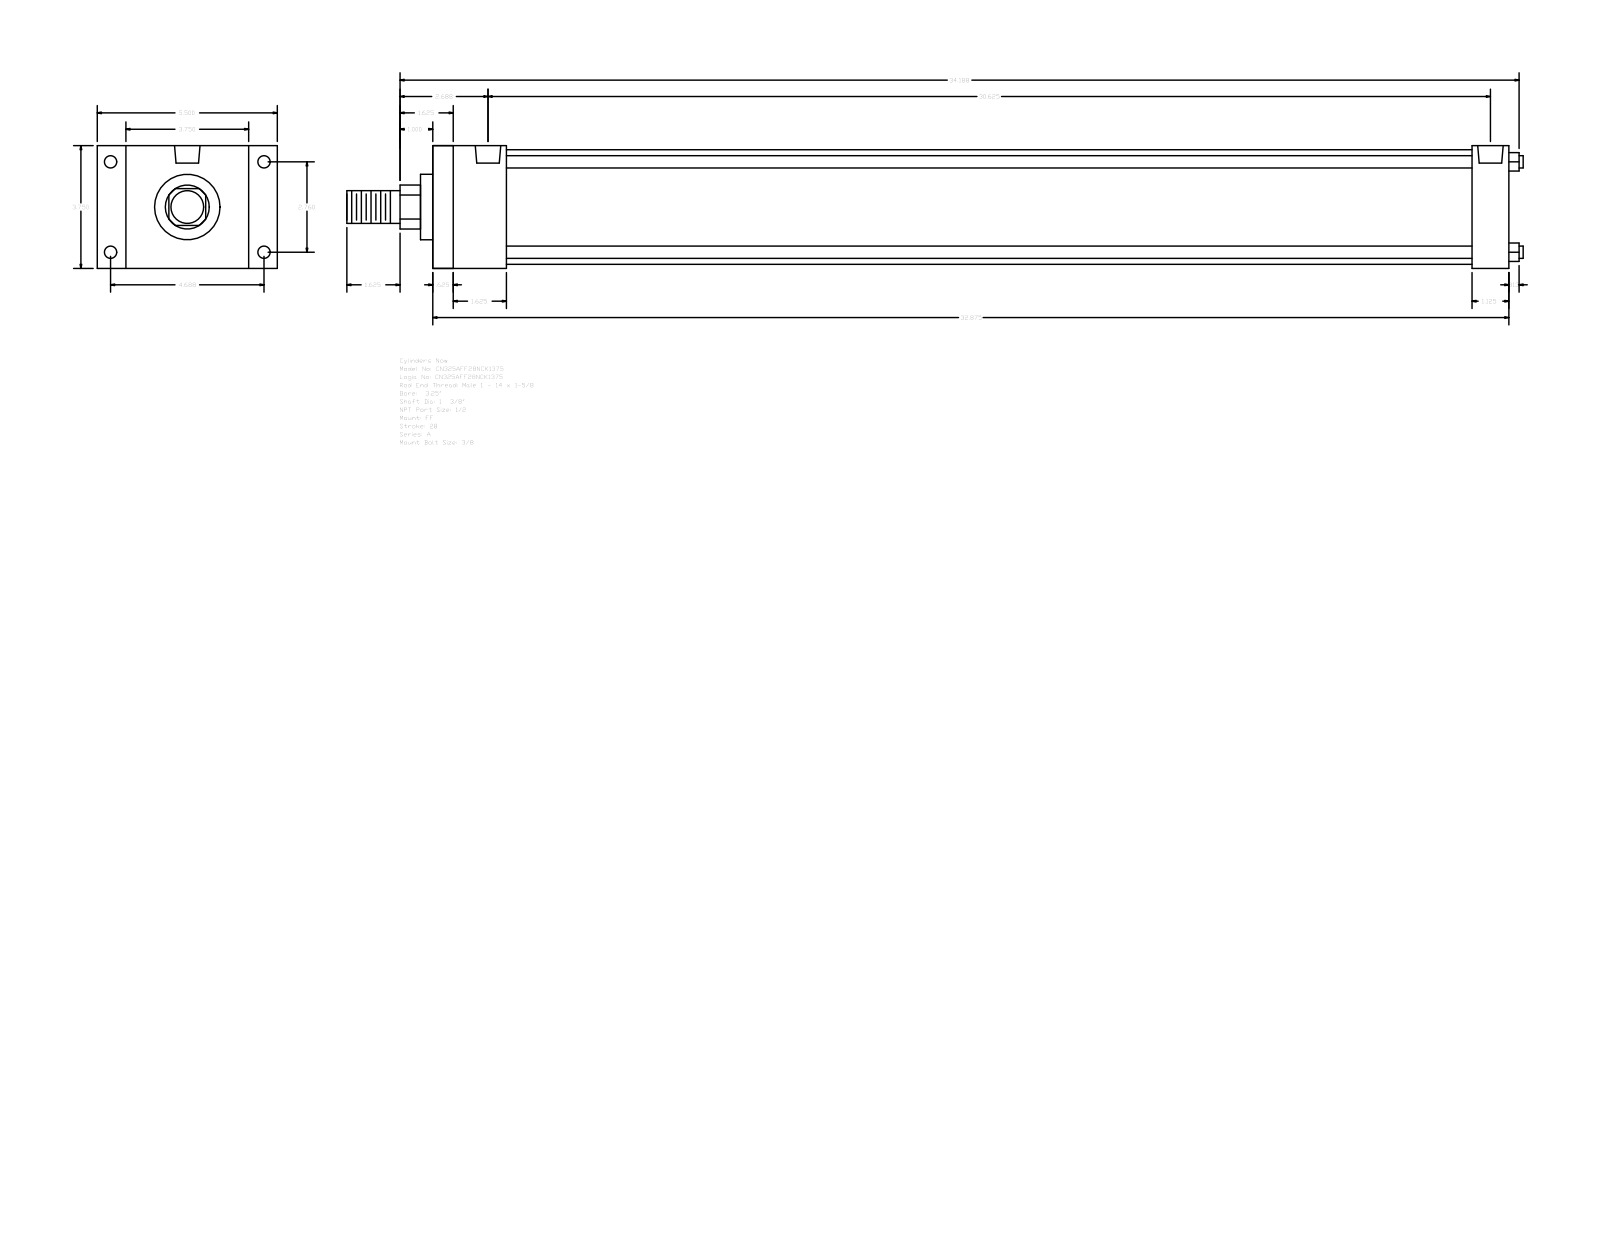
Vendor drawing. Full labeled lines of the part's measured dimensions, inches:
Part name (STEP PRODUCT): A_FF__0325_1.375
STEP written by: GSSL Pune (CONFIG_CONTROL_DESIGN)
Units: inches
Bodies: 0 solids, 92 faces (64 planar, 28 cylindrical, 0 other)
Overall size (bounding box): 35.937 × 5.5 × 3.75
Round holes (diameter × count): ⌀0.344 ×4, ⌀0.375 ×4, ⌀0.778 ×2
Round bosses / shafts (diameter × count): ⌀0.375 ×4, ⌀3.5 ×1, ⌀2 ×1, ⌀1.375 ×1, ⌀1 ×1
Partial cylindrical surfaces — rounded edges, fillets, slot ends (radius × count): R0.672 ×1
Main face-to-face distances: 3.75, 32.875, 32.25, 0.625, 2.25, 0.875, 4.625, 1.125, 31.75, 1.625
Hole centre spacings: 0.125, 2.76, 4.687, 5.439, 30.375, 30.5, 30.625
